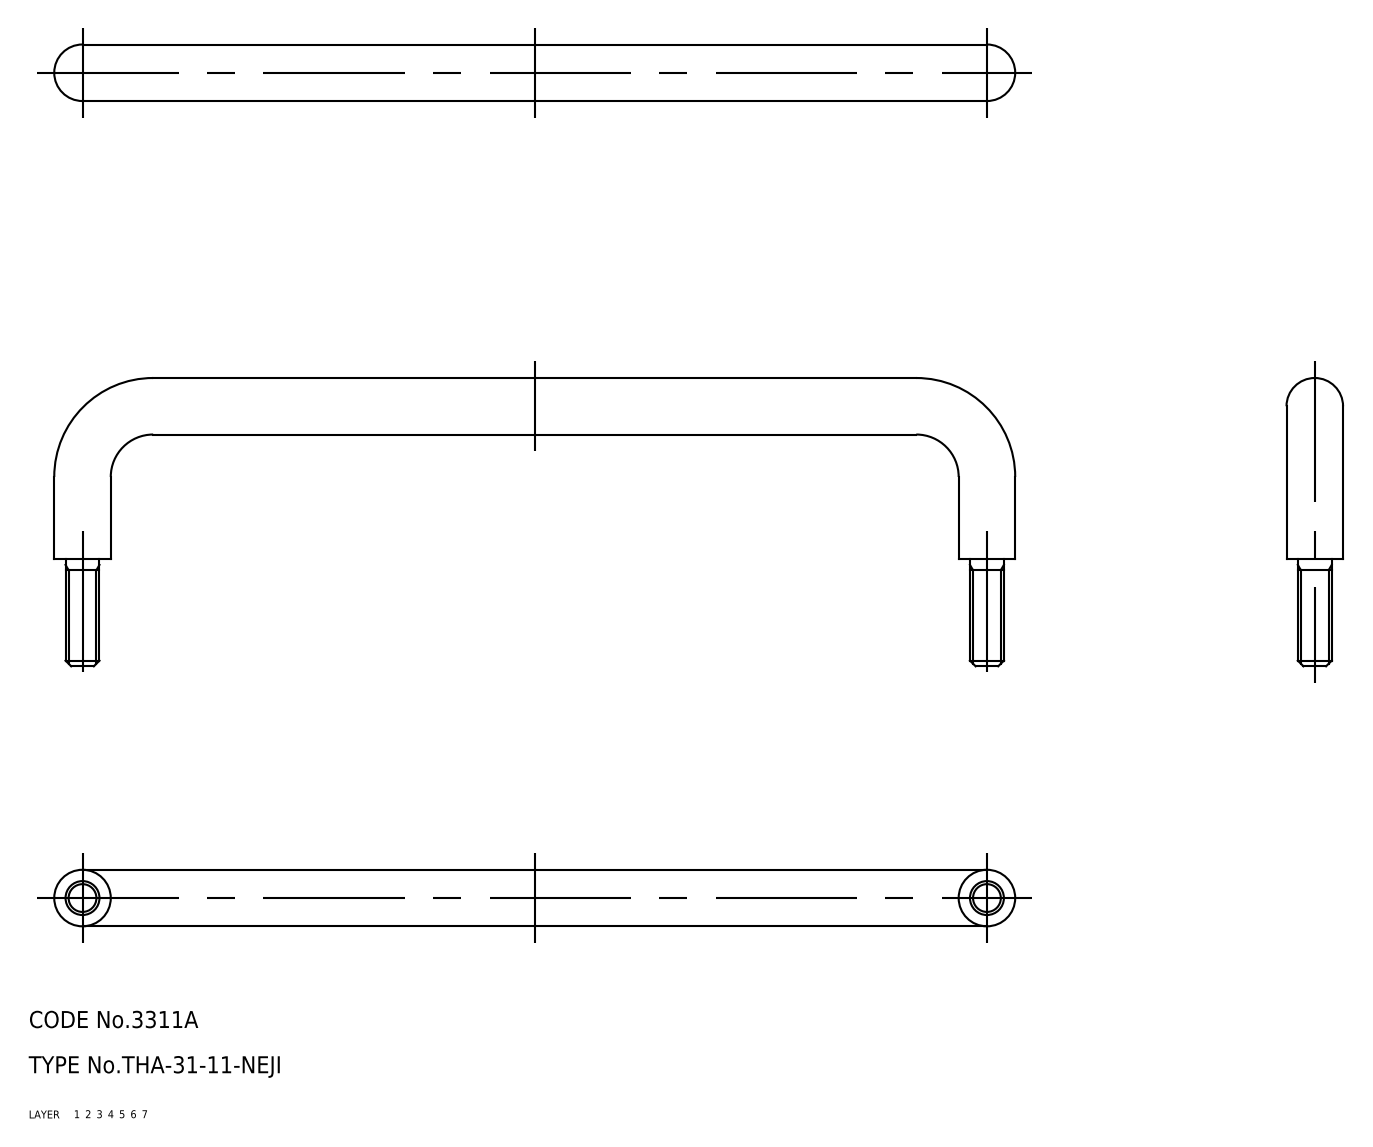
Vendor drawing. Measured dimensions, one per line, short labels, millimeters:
name: pull
written by: CADfix (AUTOMOTIVE_DESIGN)
unit: mm
bodies: 1 solid, 22 faces (0 planar, 0 cylindrical, 22 other)
size: 170 × 51 × 10
volume: 17 017 mm³; area: 7 238 mm²
